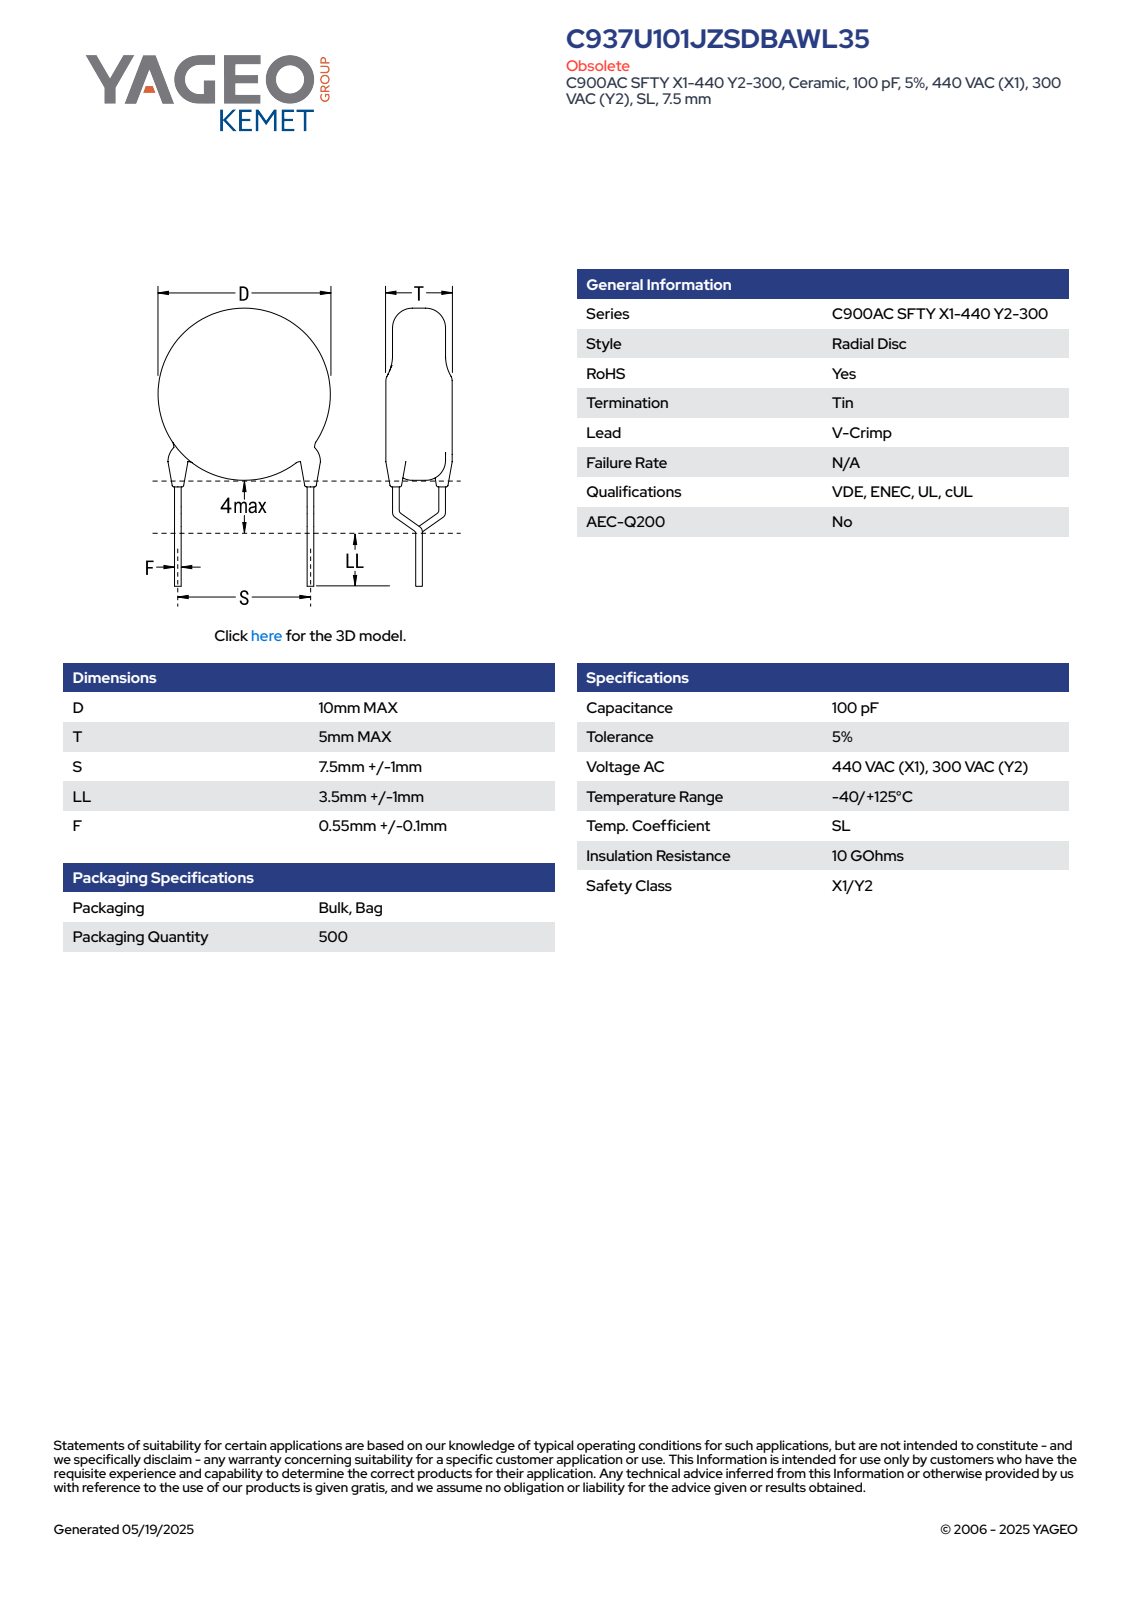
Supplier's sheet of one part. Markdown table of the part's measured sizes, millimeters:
| quantity | value |
| --- | --- |
| part name | CCD_VCC900_D10T5S7.5LL4.5F0.65 |
| STEP written by | SolidWorks 2014 (AUTOMOTIVE_DESIGN) |
| units | millimeters |
| bodies | 5 solids, 93 faces (65 planar, 16 cylindrical, 12 other) |
| overall size | 18.3 × 10 × 5 |
| volume | 388 mm³ |
| surface area | 340 mm² |
| round bosses / shafts (diameter × count) | 0.65 × 6, 10 × 1 |
| main face-to-face distances | 5, 7.4, 1.3, 13.95, 6.55, 12.65, 5.25, 0.32, 1.05, 2.68 |
